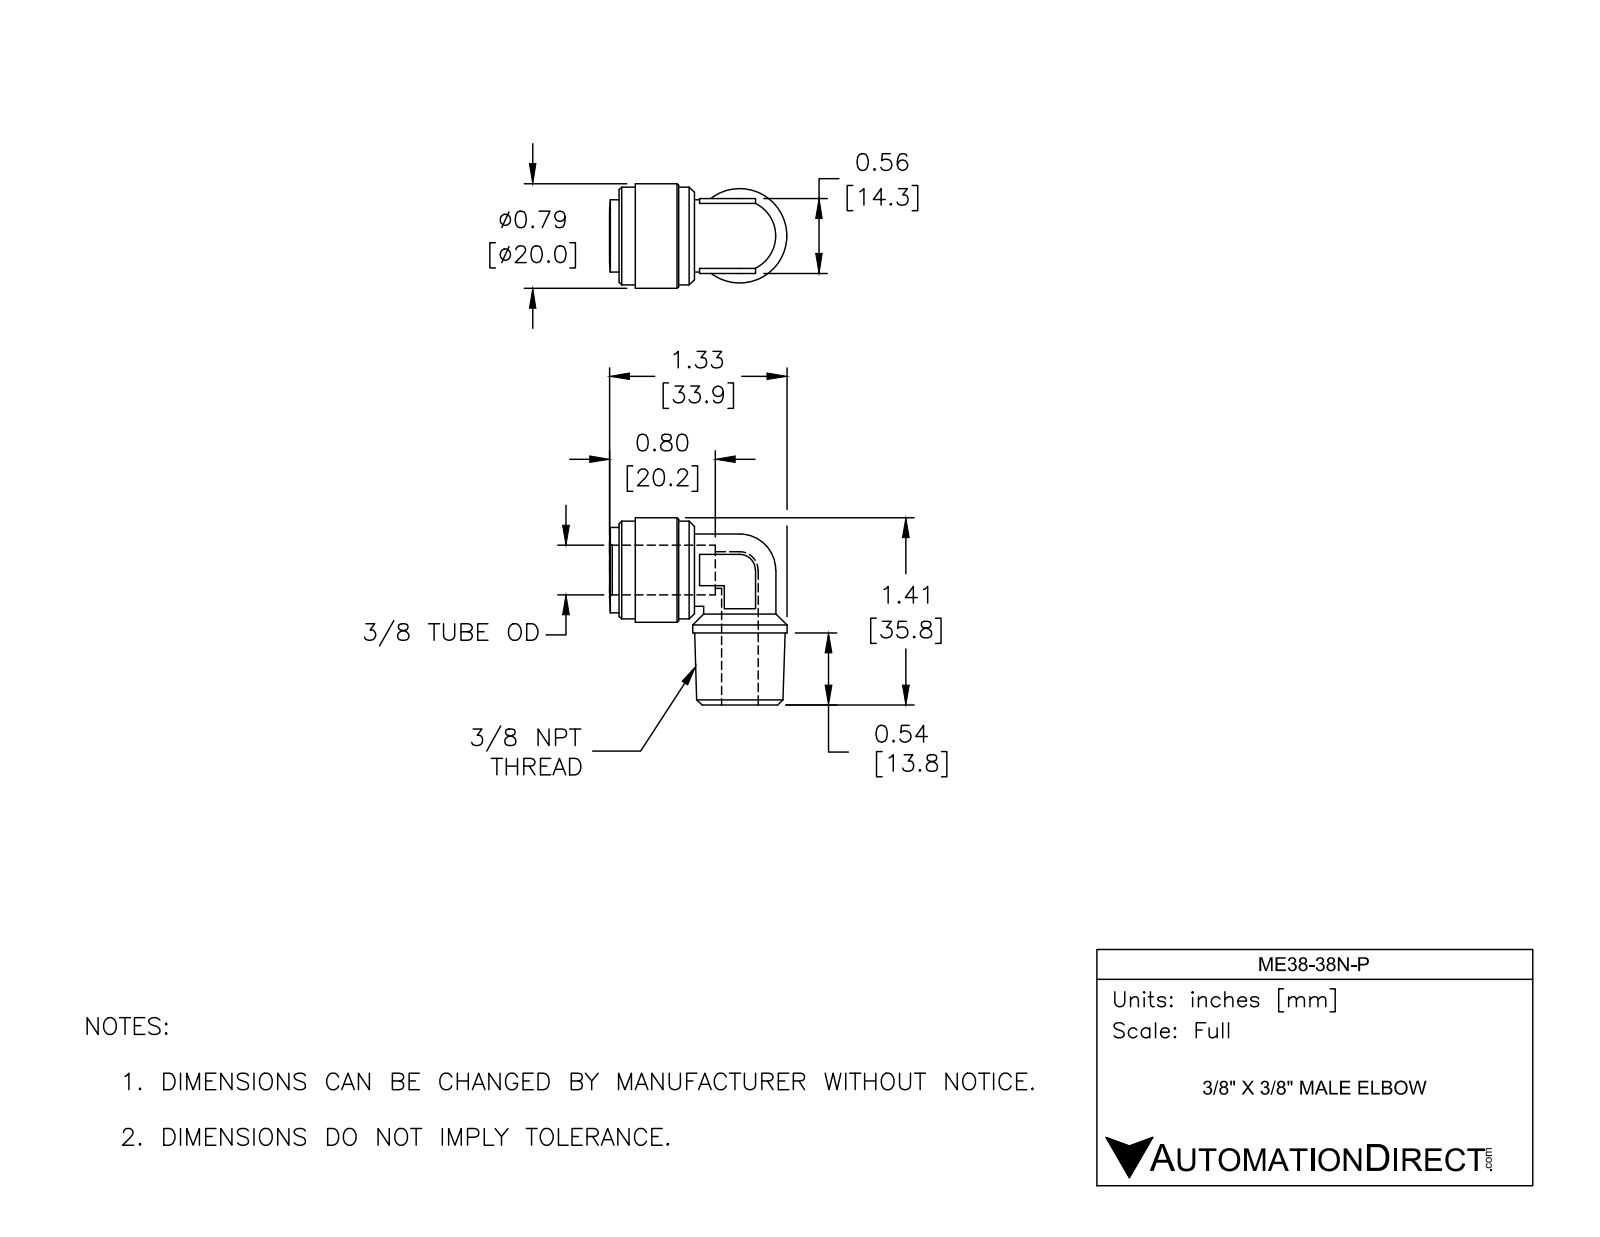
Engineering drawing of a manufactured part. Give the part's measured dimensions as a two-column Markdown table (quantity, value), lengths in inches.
| quantity | value |
| --- | --- |
| part name | ME38-38N-P |
| STEP written by | SolidWorks 2017 (AUTOMOTIVE_DESIGN) |
| units | inches |
| bodies | 1 solid, 63 faces (21 planar, 20 cylindrical, 22 other) |
| overall size | 1.409 × 1.335 × 0.787 |
| volume | 0.511 in³ |
| surface area | 6.941 in² |
| round holes (diameter × count) | 0.276 × 2, 0.374 × 1 |
| round bosses / shafts (diameter × count) | 0.543 × 2, 0.787 × 1, 0.736 × 1, 0.709 × 1 |
| partial cylindrical surfaces (radius × count) | 0.118 × 1 |
| main face-to-face distances | 0.563, 0.567, 0.122, 0.445, 0.724, 0.157, 0.602, 0.118, 0.449, 0.327 |
